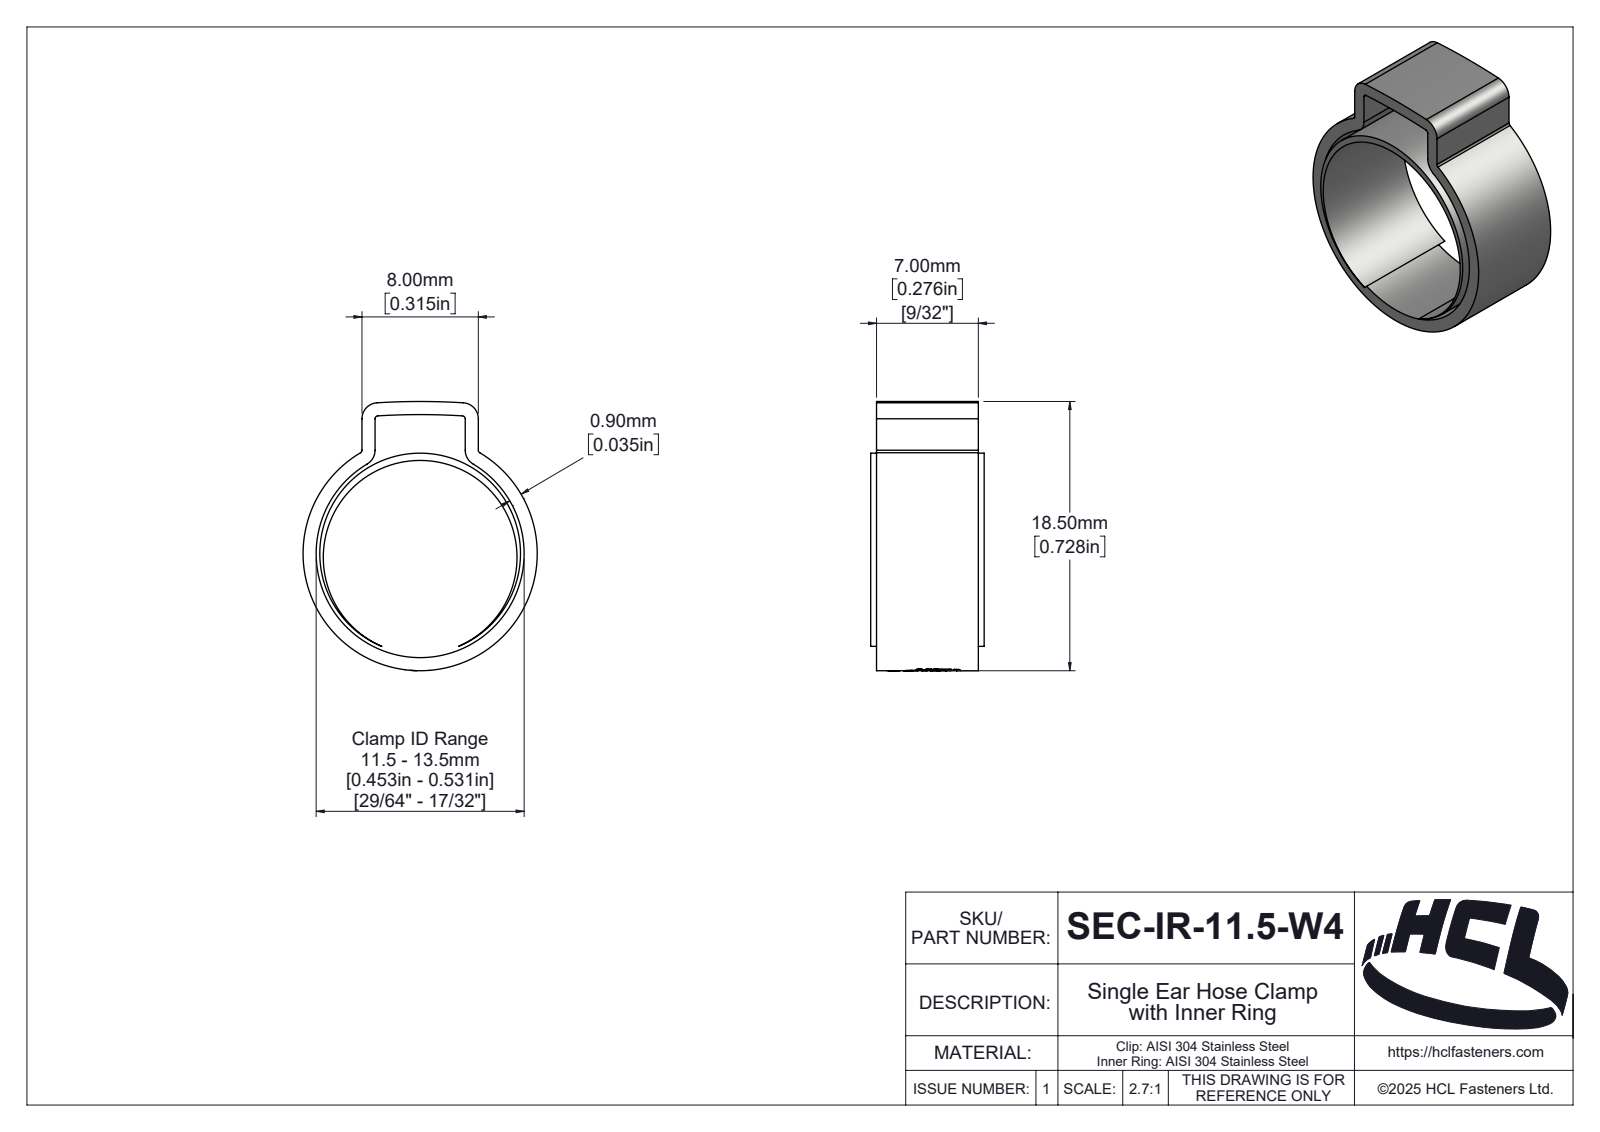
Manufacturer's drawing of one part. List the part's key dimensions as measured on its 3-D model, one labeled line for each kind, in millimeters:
Part name (STEP PRODUCT): SEC-IR-11.5-W4
STEP written by: SolidWorks 2025 (AUTOMOTIVE_DESIGN)
Units: millimetres
Bodies: 2 solids, 131 faces (10 planar, 72 cylindrical, 49 other)
Overall size (bounding box): 18.5 × 16.1 × 7.8
Volume: 415 mm³ · Surface area: 1 444 mm²
Round holes (diameter × count): ⌀13.32 ×1, ⌀14.3 ×1
Round bosses / shafts (diameter × count): ⌀16.1 ×1, ⌀13.8 ×1
Partial cylindrical surfaces — rounded edges, fillets, slot ends (radius × count): R0.2 ×4, R1.1 ×4, R0.21 ×1, R0.88 ×1, R1.09 ×1, R1.15 ×1, R1.39 ×1, R1.97 ×1
Main face-to-face distances: 7, 0.9, 7.1, 0.4, 7.4, 8, 6.2, 7.8, 3.71, 2.81
